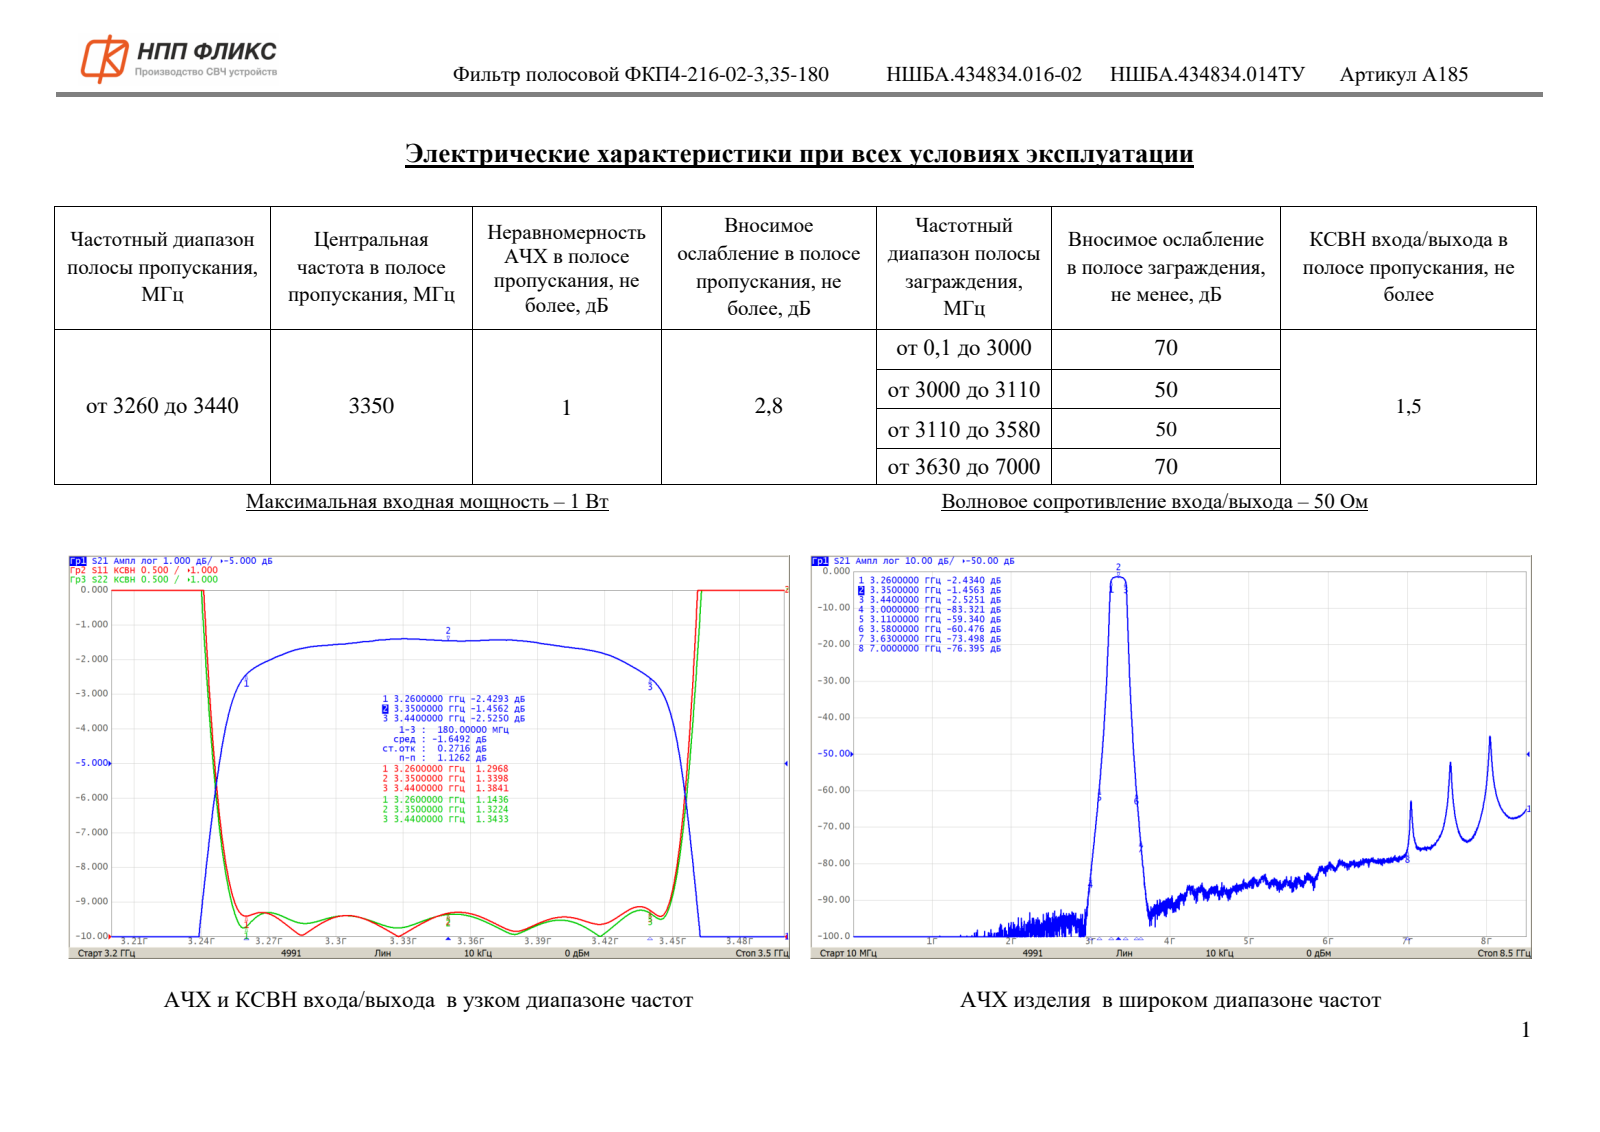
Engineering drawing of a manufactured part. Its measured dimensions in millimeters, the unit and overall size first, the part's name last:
Units: millimetres
Overall size (bounding box): 28 × 7.4 × 4.4
Round holes (diameter × count): ⌀1.5 ×6, ⌀0.95 ×1
Round bosses / shafts (diameter × count): ⌀0.86 ×1, ⌀0.2 ×1
Partial cylindrical surfaces — rounded edges, fillets, slot ends (radius × count): R1.5 ×4, R1.6 ×4, R0.2 ×3, R0.1 ×1, R0.3 ×1, R0.35 ×1
Main face-to-face distances: 4.35, 7.4, 4.4, 26.4, 0.4, 7, 0.43, 6.97, 6.57, 0.35
Hole centre spacings: 7.5, 3.76, 3.74, 11.26, 15, 11.24, 18.76
Volume: 843 mm³ · Surface area: 744 mm²
Bodies: 1 solid, 518 faces (318 planar, 28 cylindrical, 172 other)
Part name (STEP PRODUCT): НШБА.434834.016-02_Фильтр ФКП4-216-02-3,35-180
STEP written by: ASCON Math Kernel (CONFIG_CONTROL_DESIGN)
